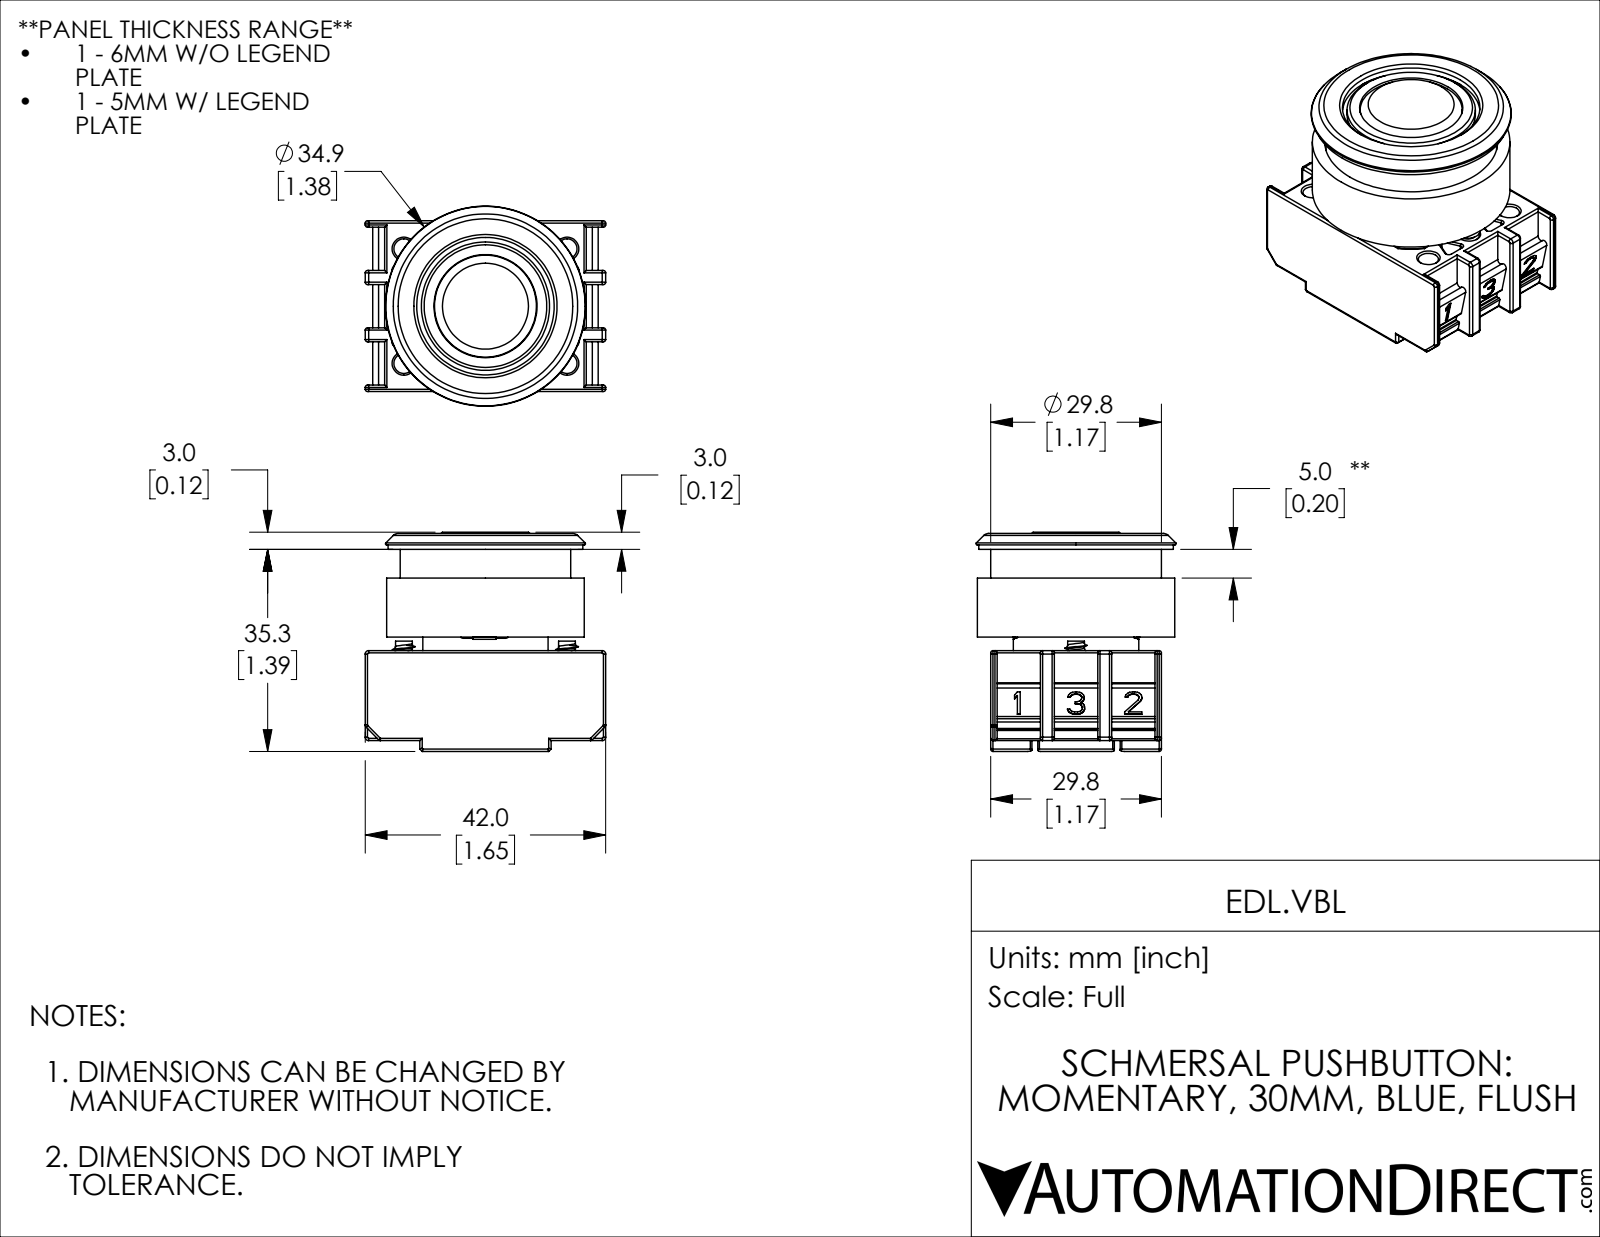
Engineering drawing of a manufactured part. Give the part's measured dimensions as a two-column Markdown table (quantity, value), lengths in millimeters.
| quantity | value |
| --- | --- |
| part name | EDL.VBL |
| STEP written by | SolidWorks 2019 (CONFIG_CONTROL_DESIGN) |
| units | millimeters |
| bodies | 5 solids, 1372 faces (506 planar, 465 cylindrical, 401 other) |
| overall size | 42 × 38.25 × 34.93 |
| volume | 25 195 mm³ |
| surface area | 19 662 mm² |
| round holes (diameter × count) | 3.5 × 6, 5.15 × 6, 10.4 × 1, 13.1 × 1, 18 × 1, 24 × 1, 24.2 × 1, 27 × 1, 30.2 × 1 |
| round bosses / shafts (diameter × count) | 4.8 × 2, 2.93 × 2, 34.5 × 1, 34 × 1, 29.8 × 1, 22.4 × 1, 21.9 × 1, 17.8 × 1 |
| partial cylindrical surfaces (radius × count) | 0.4 × 112, 0.3 × 48, 0.2 × 32, 0.6 × 8, 0.5 × 6, 0.1 × 2, 0.6 × 2, 0.8 × 2 |
| main face-to-face distances | 29.8, 16.1, 19.95, 2.35, 10, 5, 1.9, 18.45, 10.3, 15.7 |
| hole center spacings | 10, 17.41, 30.2, 28.5, 14.25, 20, 34.82 |
